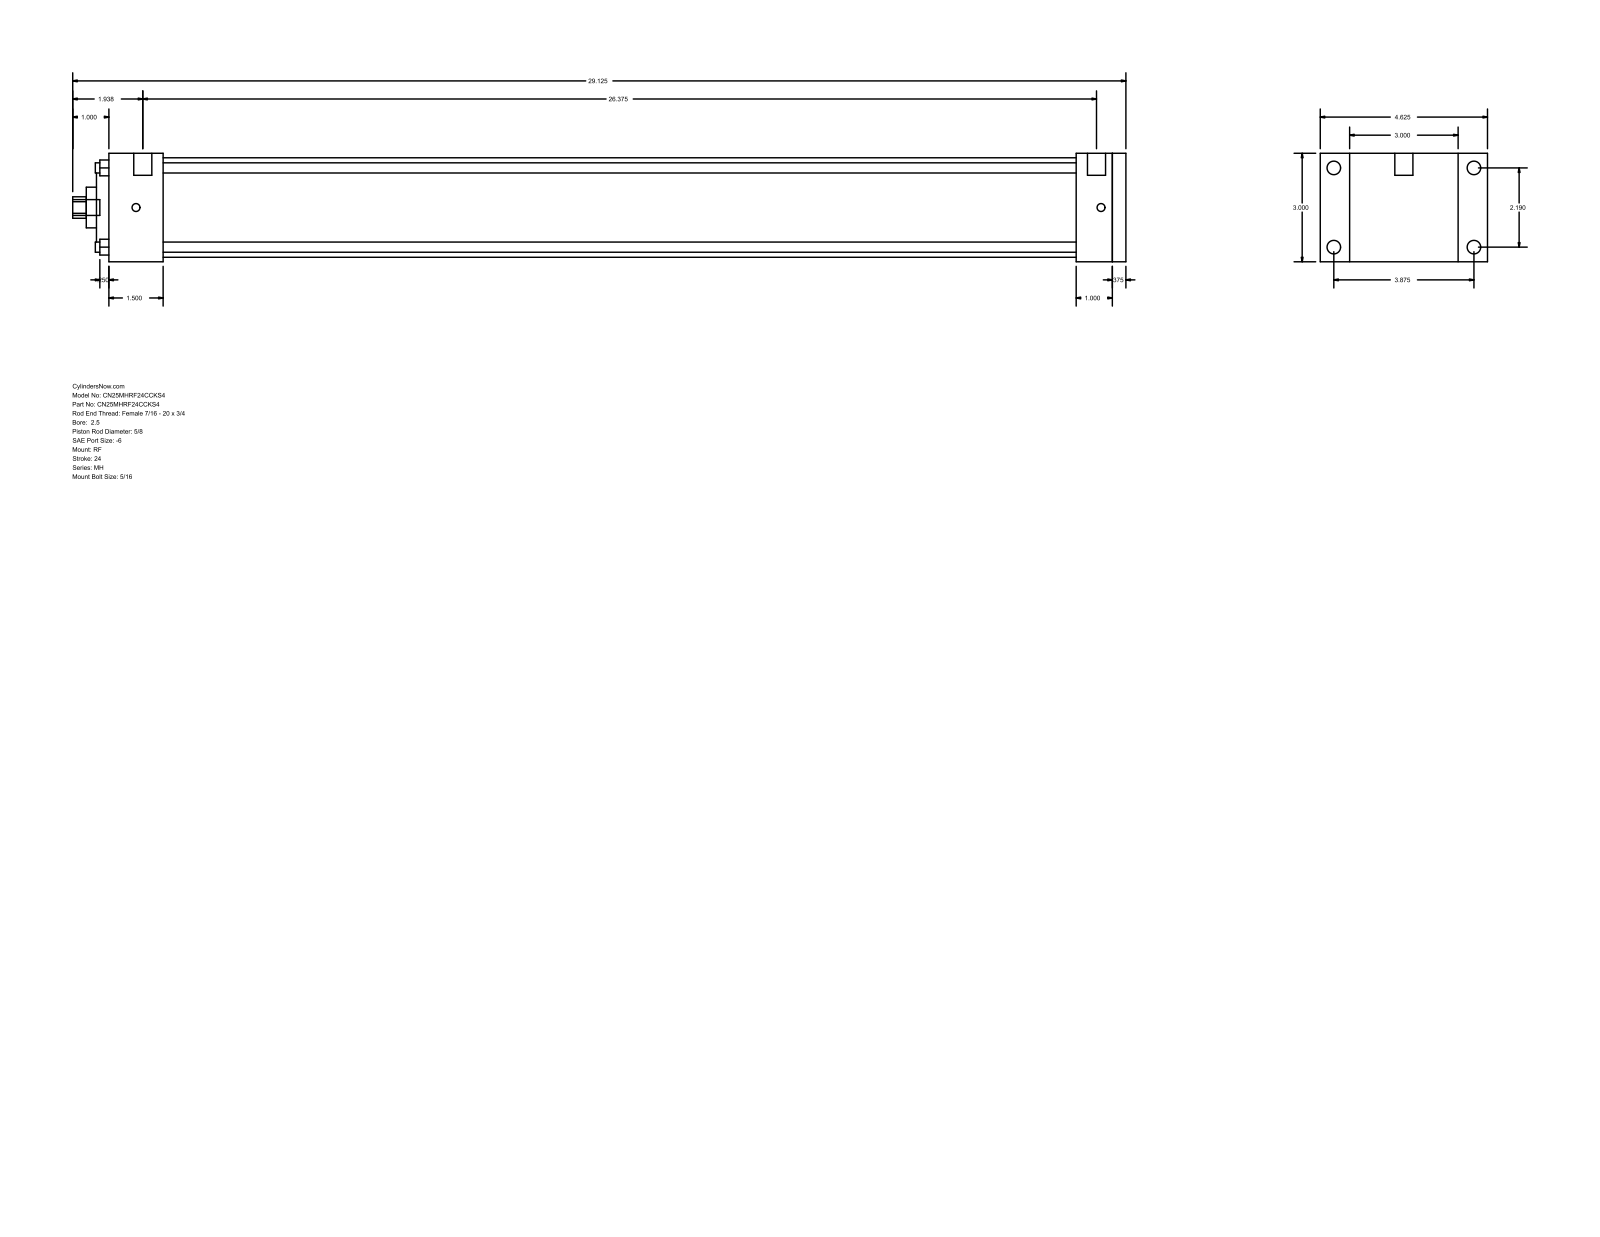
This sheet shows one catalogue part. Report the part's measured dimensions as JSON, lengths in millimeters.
{"part_name": "MH_RF__0250_0.625", "step_written_by": "GSSL Pune (CONFIG_CONTROL_DESIGN)", "units": "millimeters", "bodies": {"solids": 0, "faces": 94, "planar": 65, "cylindrical": 29, "other": 0}, "overall_size": [739.77, 117.47, 76.2], "round_holes": [[7.14, 4], [15.88, 1], [28.57, 1], [55.55, 1], [69.85, 1]], "round_bosses_or_shafts": [[9.53, 4], [5.56, 4], [12.7, 2], [11.11, 1]], "partial_cylinders_radius": [[7.54, 1]], "face_to_face_distances": [76.2, 9.52, 714.37, 704.85, 25.4, 679.45, 34.92, 38.1, 641.35, 666.75], "hole_center_spacings": [39.33, 55.62, 78.66]}
